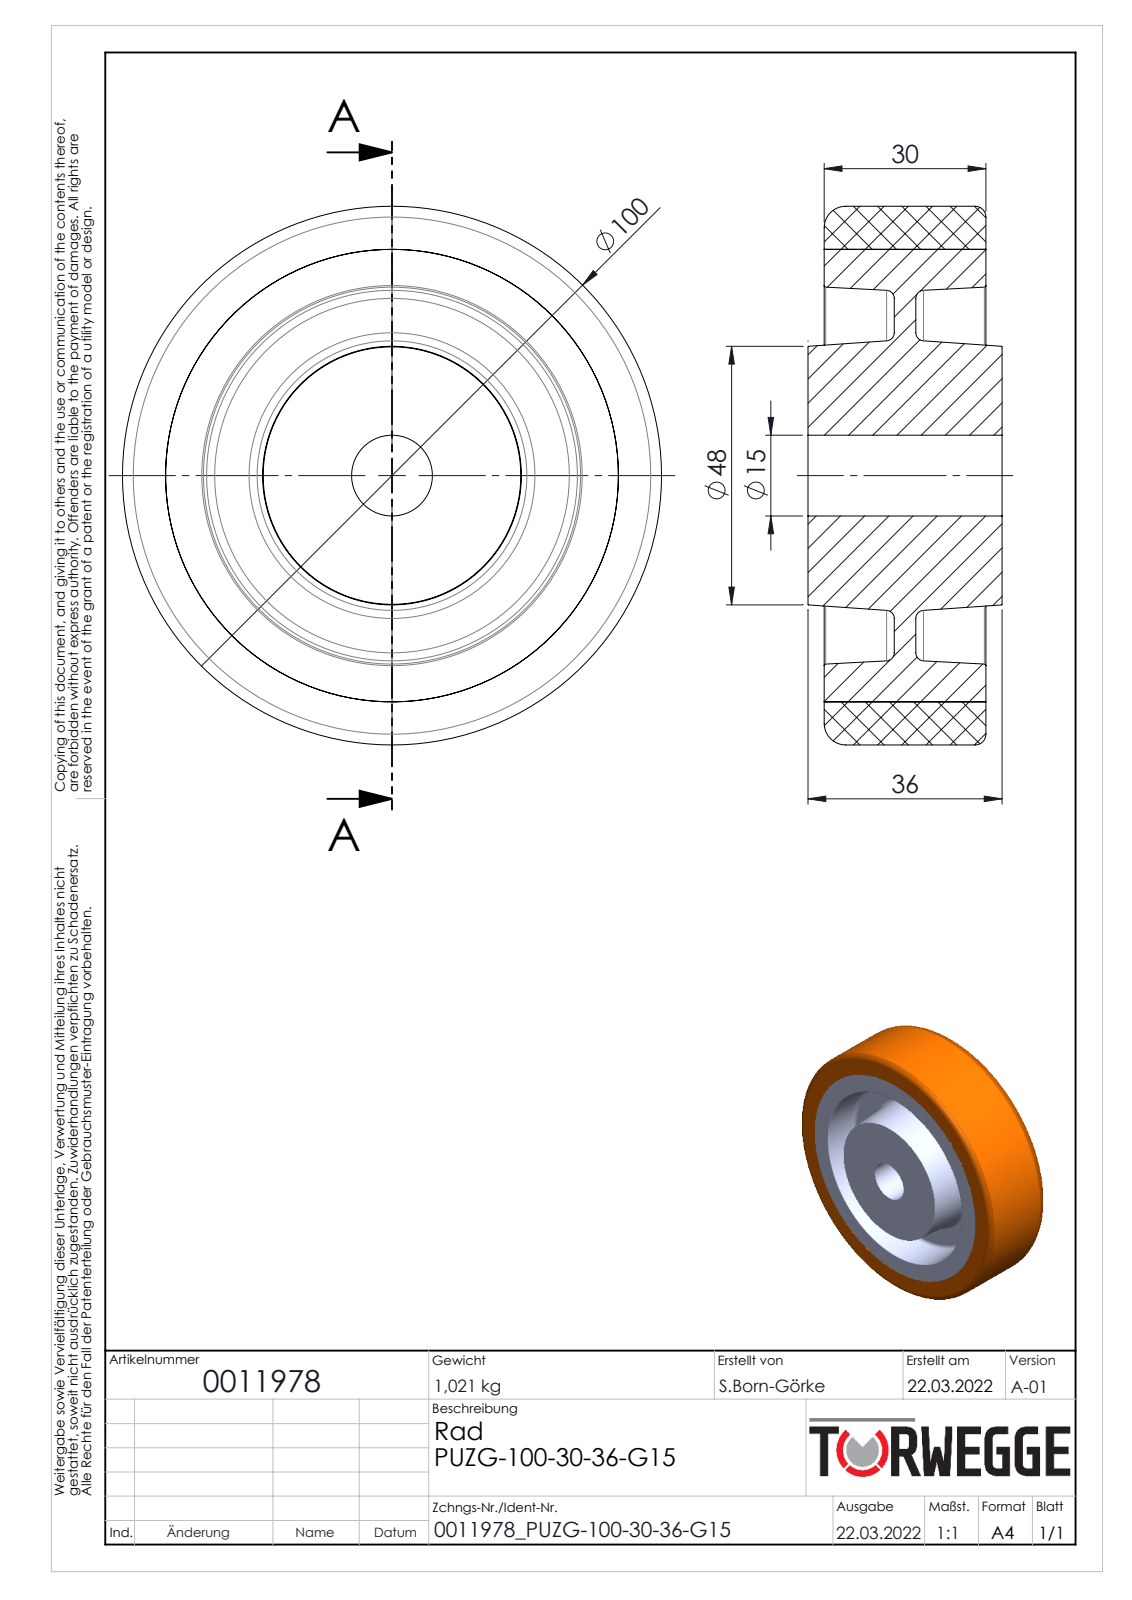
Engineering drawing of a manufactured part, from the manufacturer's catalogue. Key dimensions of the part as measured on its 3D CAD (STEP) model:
Part name (STEP PRODUCT): 0011978
STEP written by: SolidWorks 2020 (AUTOMOTIVE_DESIGN)
Units: millimetres
Bodies: 2 solids, 44 faces (8 planar, 8 cylindrical, 28 other)
Overall size (bounding box): 100 × 100 × 36
Volume: 190 758 mm³ · Surface area: 50 985 mm²
Round holes (diameter × count): ⌀15 ×1, ⌀84 ×1
Round bosses / shafts (diameter × count): ⌀100 ×1
Main face-to-face distances: 3, 33, 30, 16, 20, 13, 17, 36, 4
